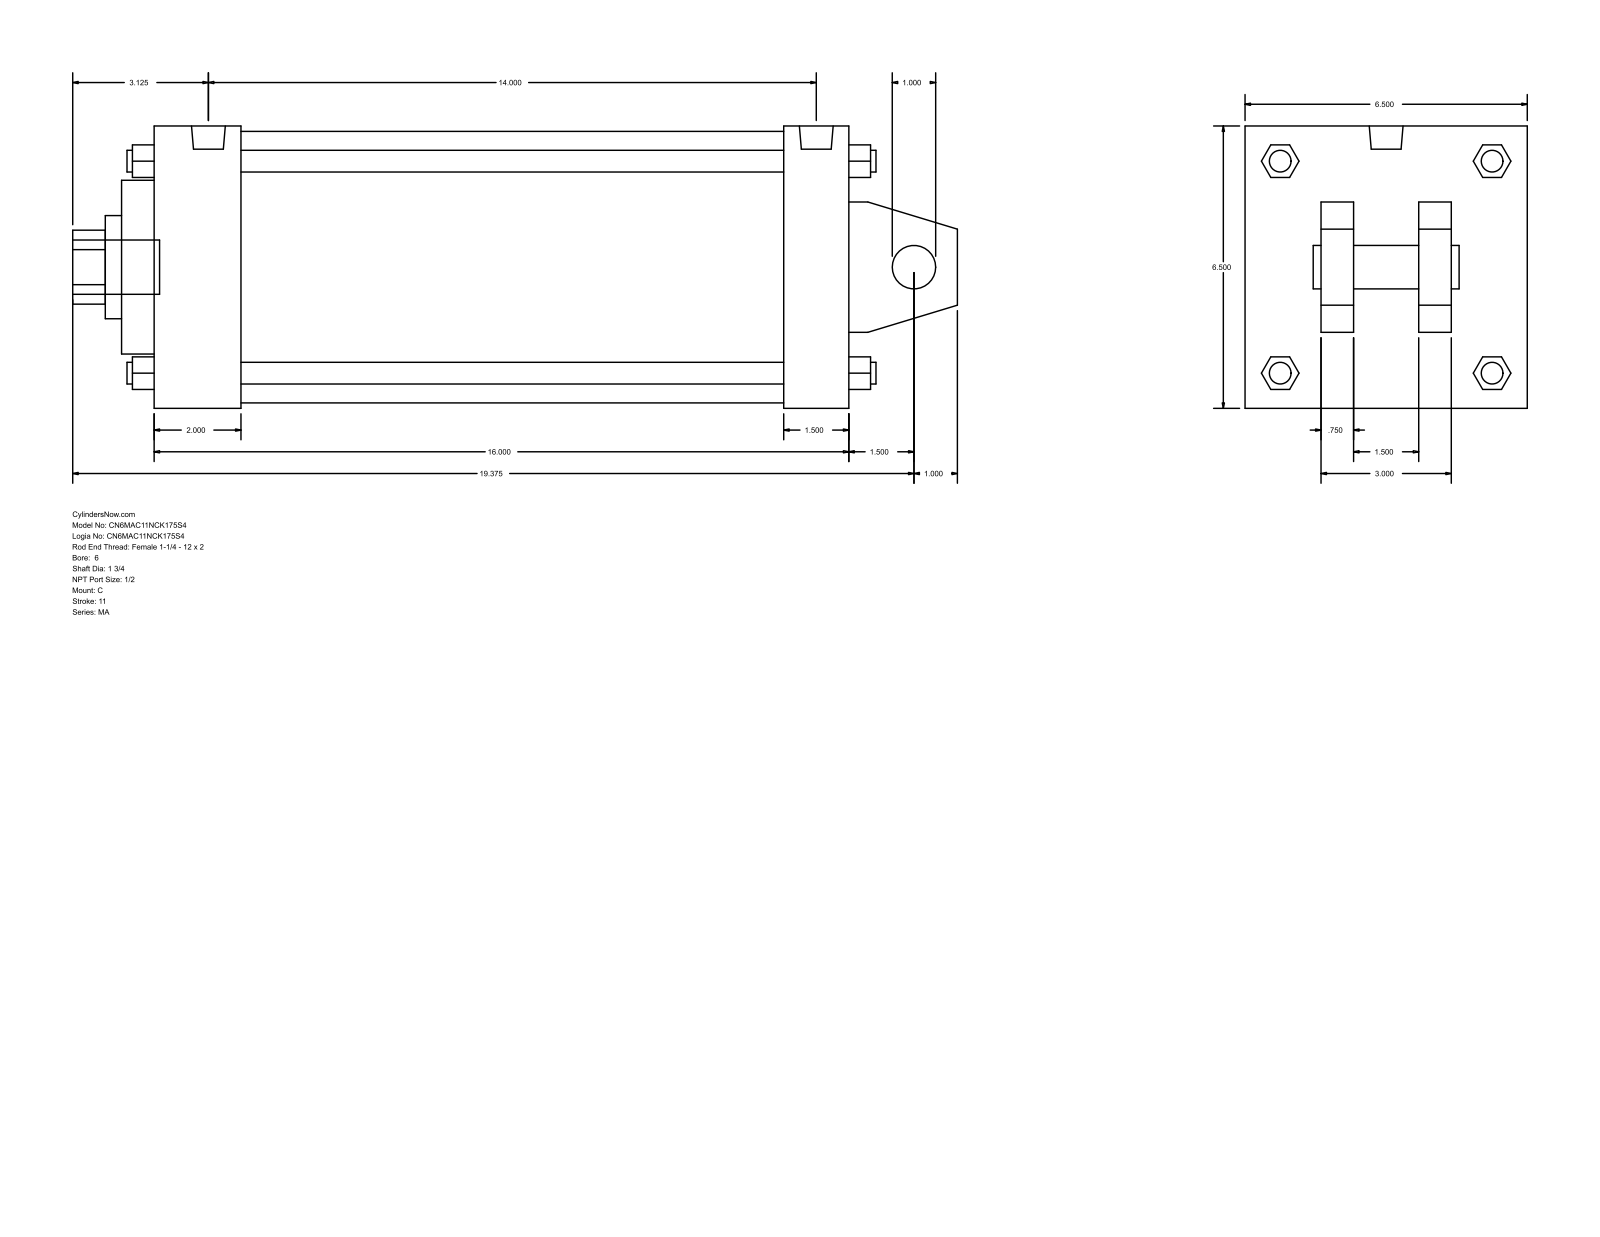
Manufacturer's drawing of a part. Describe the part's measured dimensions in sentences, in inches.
The part is named "MA_C__0600_1.75". Its 3-D file was written by "GSSL Pune (CONFIG_CONTROL_DESIGN)". It is 0 solids with 141 faces: 109 planar, 32 cylindrical and 0 other. Overall it measures 20.375 by 6.5 by 6.5 inches. Round holes: 1 of diameter 1, 1 of diameter 1.75, 1 of diameter 2.375, 1 of diameter 4, 1 of diameter 6.25. Round bosses or shafts: 4 of diameter 0.687, 4 of diameter 0.5, 2 of diameter 0.778, 1 of diameter 1.25. Partial cylindrical surfaces (rounded edges, fillets, slot ends): 1 of radius 0.852. The main face-to-face distances are 6.5, 16, 0.75, 2.5, 4, 2, 4.75, 1.75, 14.5, 2.25.
